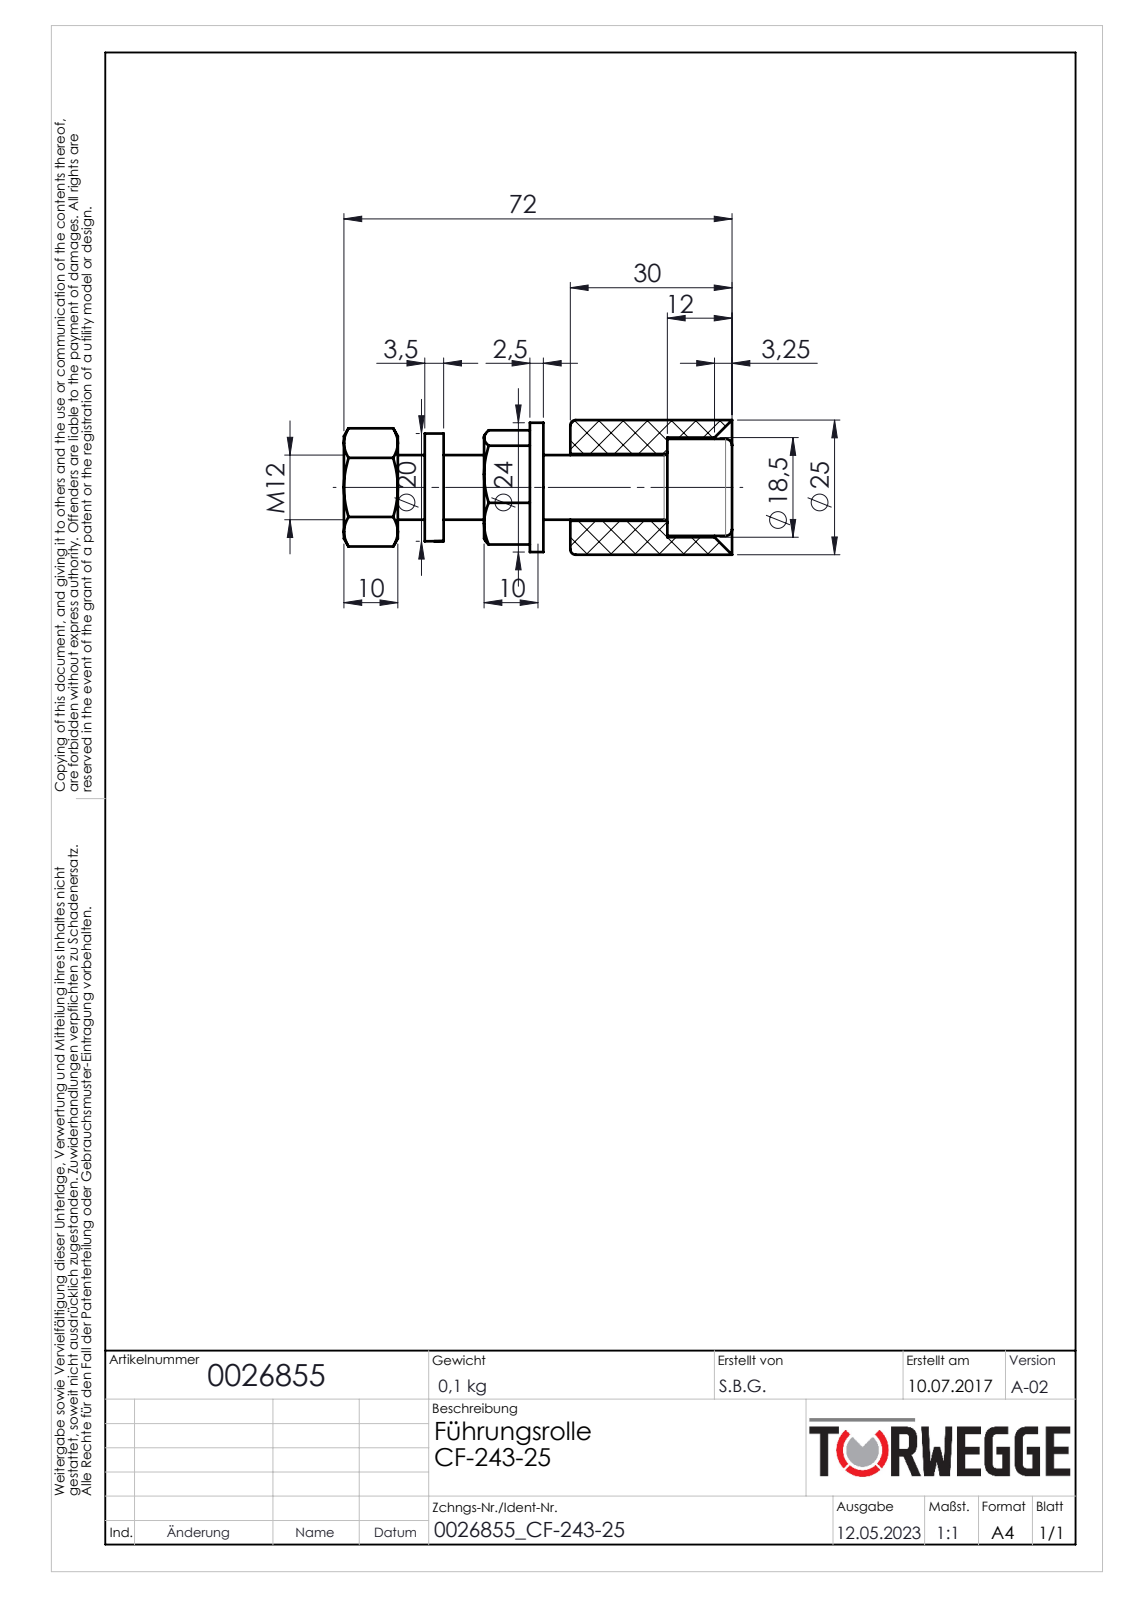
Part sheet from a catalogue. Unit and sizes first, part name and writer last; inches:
Units: inches
Overall size (bounding box): 2.835 × 0.984 × 0.984
Round holes (diameter × count): ⌀0.409 ×1, ⌀0.488 ×1, ⌀0.512 ×1, ⌀0.728 ×1
Round bosses / shafts (diameter × count): ⌀0.984 ×1, ⌀0.945 ×1, ⌀0.787 ×1, ⌀0.709 ×1, ⌀0.472 ×1
Main face-to-face distances: 0.63, 0.197, 0.295, 0.748, 1.063, 0.728, 0.394, 1.024, 0.335, 0.433
Volume: 1.471 in³ · Surface area: 19.25 in²
Bodies: 6 solids, 105 faces (39 planar, 22 cylindrical, 44 other)
Part name (STEP PRODUCT): 0026855
STEP written by: SolidWorks 2020 (AUTOMOTIVE_DESIGN)
